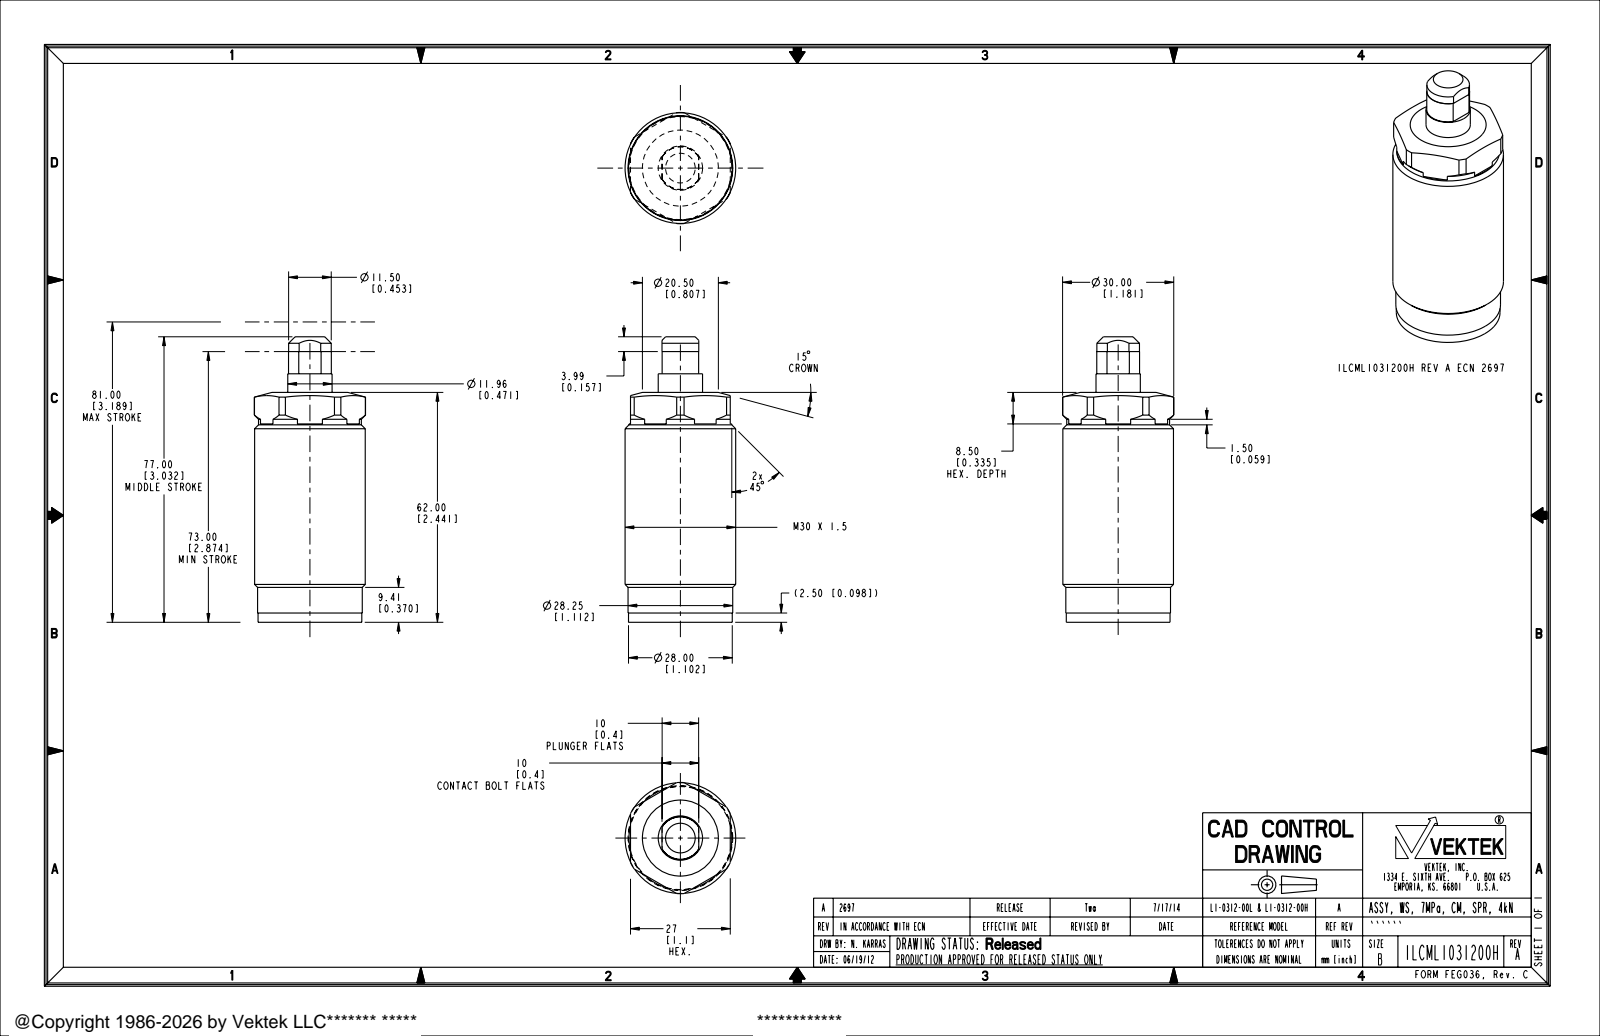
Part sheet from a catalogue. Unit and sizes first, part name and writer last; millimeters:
Units: millimetres
Overall size (bounding box): 77 × 30 × 29.85
Round bosses / shafts (diameter × count): ⌀29.85 ×1, ⌀28.25 ×1, ⌀28 ×1, ⌀27.75 ×1, ⌀11.96 ×1
Partial cylindrical surfaces — rounded edges, fillets, slot ends (radius × count): R5.75 ×1, R5.78 ×1, R15 ×1
Main face-to-face distances: 26.92, 62, 8.54, 18.38, 77, 15, 8.5, 9.84, 18.42, 9.88
Volume: 43 212 mm³ · Surface area: 7 498 mm²
Bodies: 1 solid, 59 faces (25 planar, 20 cylindrical, 14 other)
Part name (STEP PRODUCT): ILCML1031200H
STEP written by: PRO/ENGINEER BY PARAMETRIC TECHNOLOGY CORPORATION, 2013320 (AUTOMOTIVE_DESIGN)
